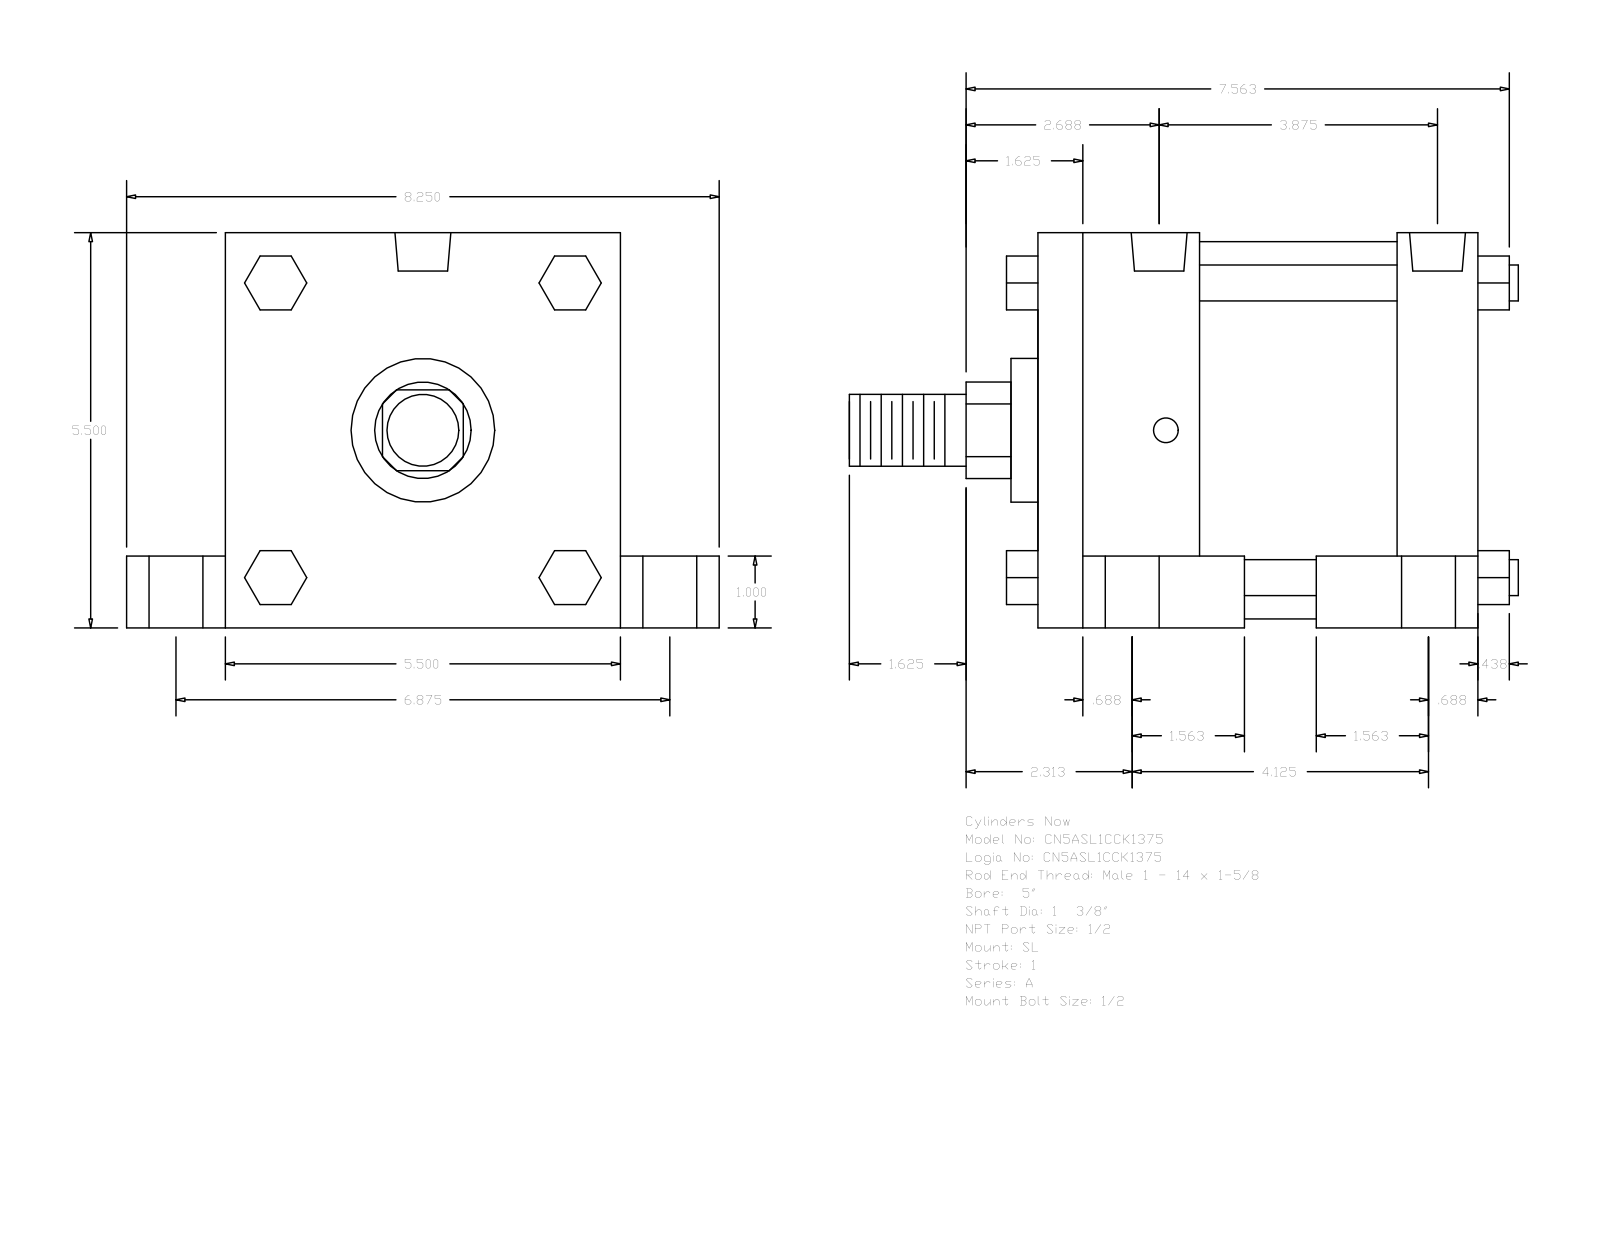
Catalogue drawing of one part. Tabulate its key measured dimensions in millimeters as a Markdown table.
| quantity | value |
| --- | --- |
| part name | A_SL__0500_1.375 |
| STEP written by | GSSL Pune (CONFIG_CONTROL_DESIGN) |
| units | millimeters |
| bodies | 0 solids, 150 faces (114 planar, 36 cylindrical, 0 other) |
| overall size | 236.54 × 209.55 × 139.7 |
| round holes (diameter × count) | 8.73 × 4, 19.05 × 4, 25.4 × 4, 19.77 × 2 |
| round bosses / shafts (diameter × count) | 12.7 × 4, 133.35 × 1, 50.8 × 1, 34.92 × 1, 25.4 × 1 |
| partial cylindrical surfaces (radius × count) | 17.06 × 1 |
| main face-to-face distances | 139.7, 155.57, 57.15, 28.57, 25.4, 114.3, 34.93, 174.63, 98.42, 69.85 |
| hole center spacings | 2.39, 87.31, 87.37, 87.83, 88.12, 93.65, 96.04, 104.77 |
